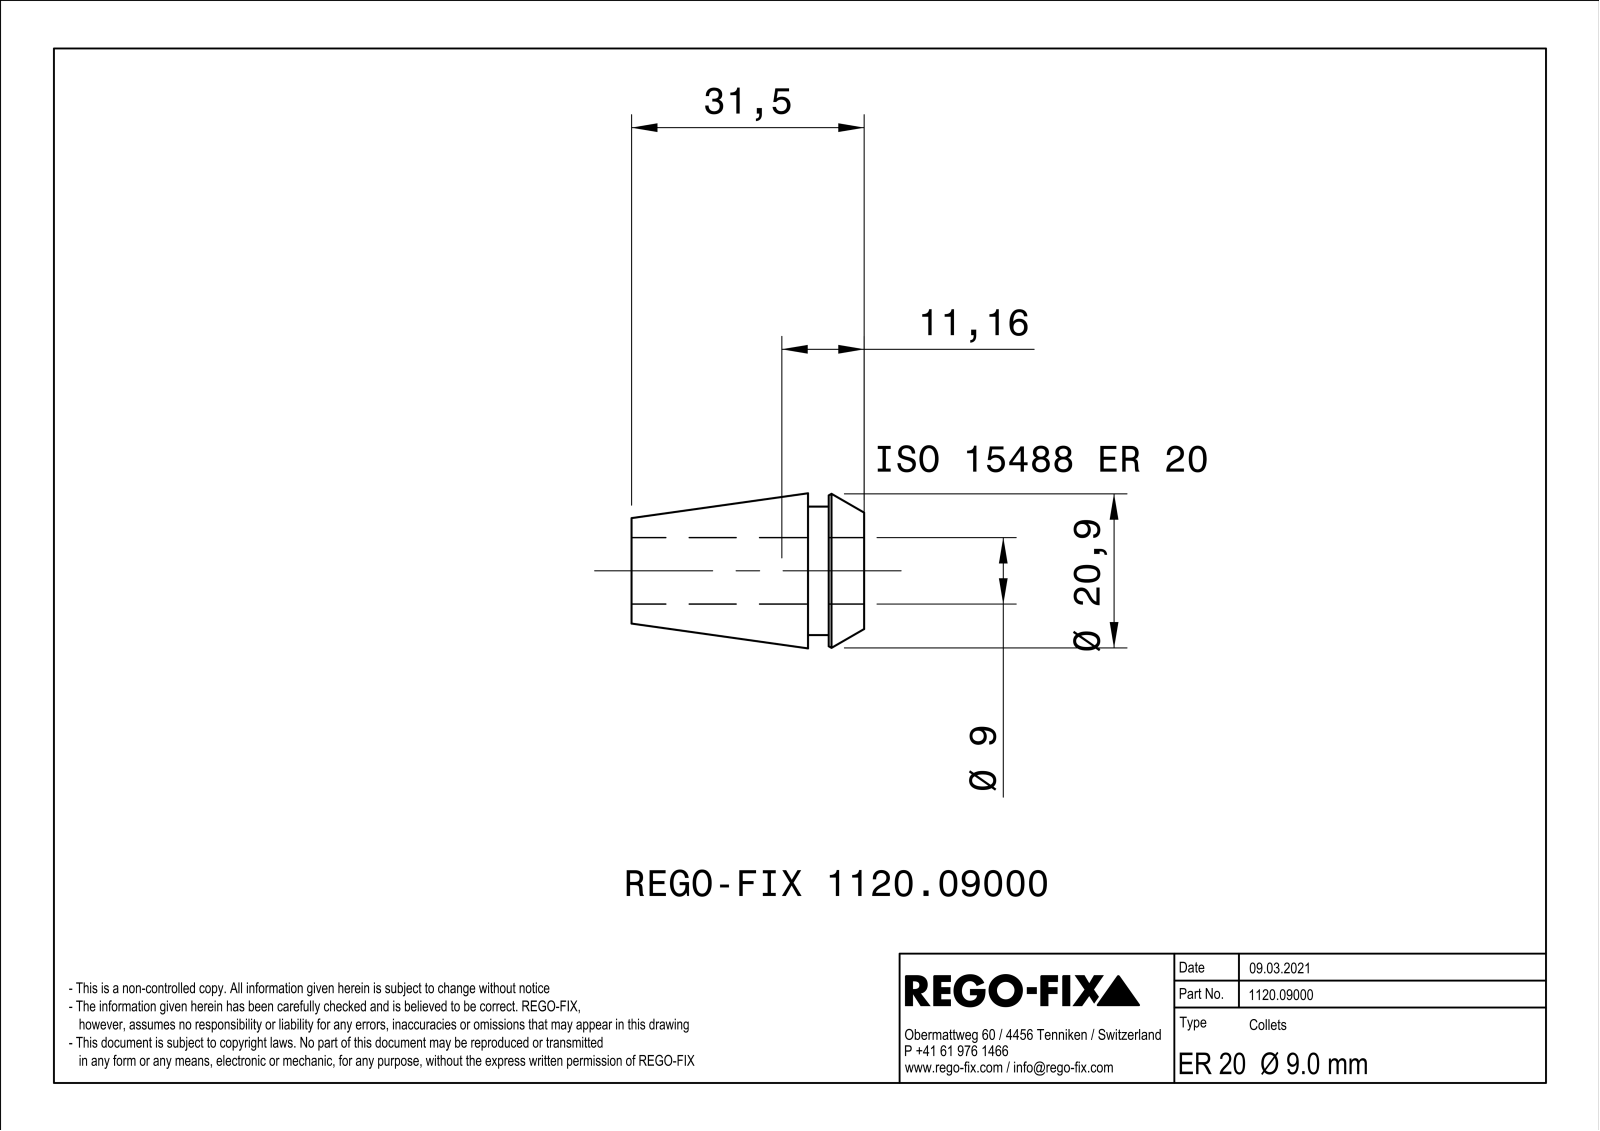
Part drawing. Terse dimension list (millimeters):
name: NOCUT
written by: SIEMENS PLM Software Solid Edge ST10 (AUTOMOTIVE_DESIGN)
unit: mm
bodies: 1 solid, 177 faces (88 planar, 9 cylindrical, 80 other)
size: 31.5 × 20.99 × 20.99
volume: 4 706 mm³; area: 6 450 mm²
holes: 1× ⌀9
bosses: 1× ⌀17.4
face distances: 0.6, 7.6, 4.8, 2.8, 31.5, 26.7, 23.9, 5.5, 0.7, 2.1
